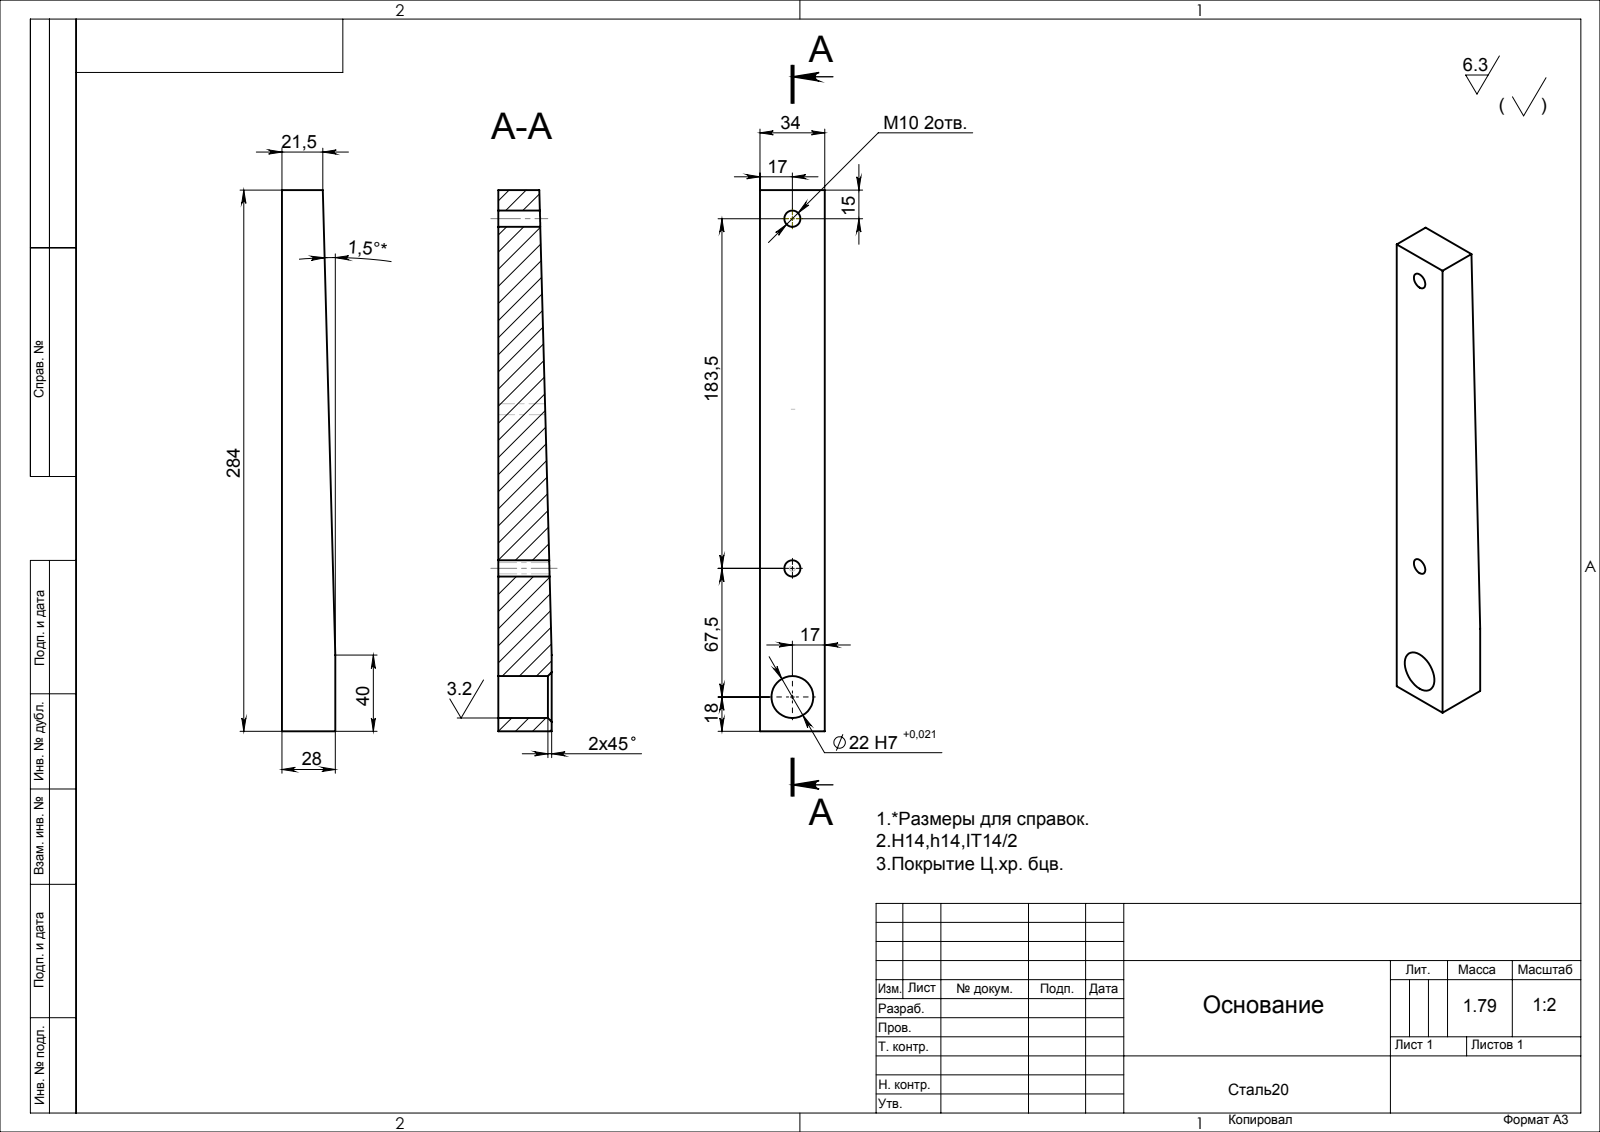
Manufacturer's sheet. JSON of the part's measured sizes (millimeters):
{"part_name": "ОСНОВАНИЕ", "step_written_by": "Mechanical Desktop 2009 (CONFIG_CONTROL_DESIGN)", "units": "millimeters", "bodies": {"solids": 1, "faces": 78, "planar": 26, "cylindrical": 52, "other": 0}, "overall_size": [360, 230, 25], "volume_mm3": 1799000, "surface_area_mm2": 199659, "round_holes": [[4.92, 10], [8.91, 4], [11, 4], [32, 4]], "partial_cylinders_radius": [[5, 8]], "face_to_face_distances": [25, 230, 100, 360, 130, 65, 13, 12, 95, 30], "hole_center_spacings": [40, 100, 140, 180, 64.03, 98.49, 107.7, 145.6]}
